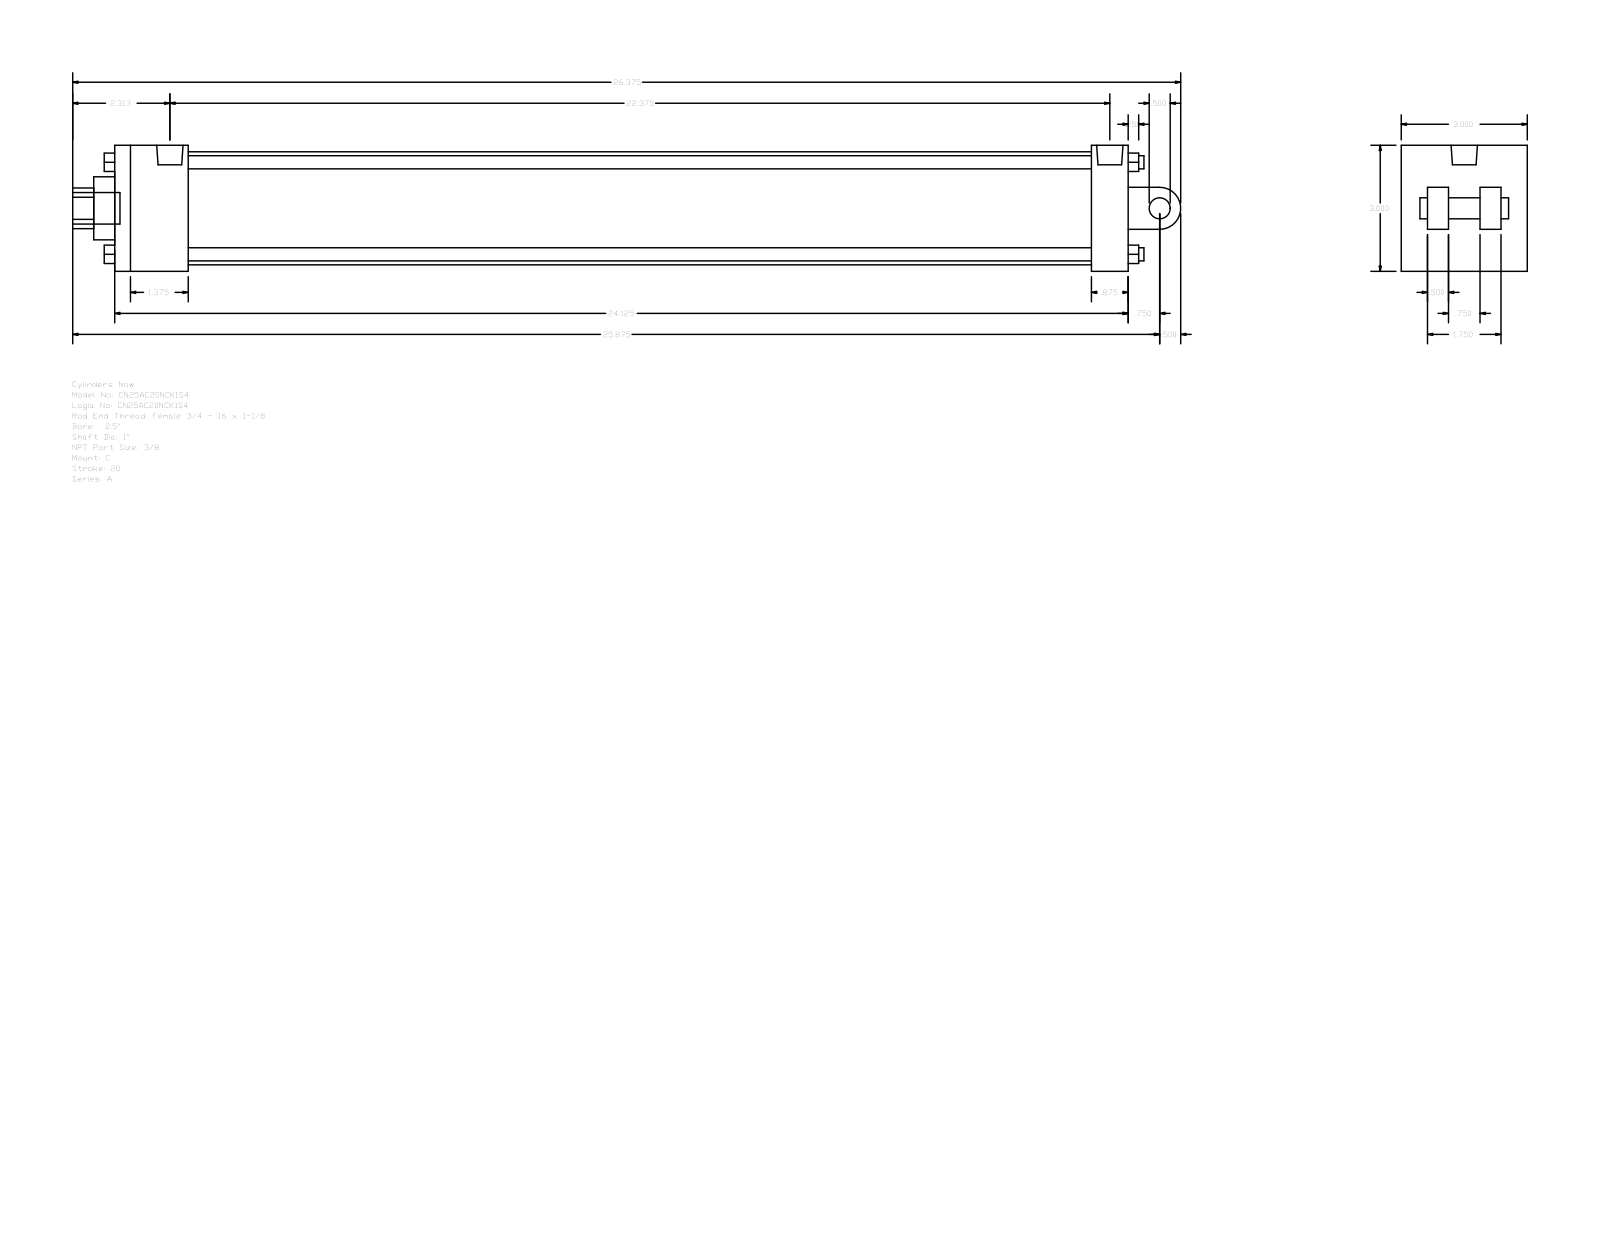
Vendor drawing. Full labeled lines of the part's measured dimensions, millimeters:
Part name (STEP PRODUCT): A_C__0250_1
STEP written by: GSSL Pune (CONFIG_CONTROL_DESIGN)
Units: millimetres
Bodies: 0 solids, 135 faces (102 planar, 33 cylindrical, 0 other)
Overall size (bounding box): 669.92 × 76.2 × 76.2
Round holes (diameter × count): ⌀5.56 ×2, ⌀15.93 ×1, ⌀25.4 ×1, ⌀38.1 ×1, ⌀68.33 ×1
Round bosses / shafts (diameter × count): ⌀7.94 ×4, ⌀5.56 ×2, ⌀19.05 ×1, ⌀15.93 ×1, ⌀12.7 ×1
Partial cylindrical surfaces — rounded edges, fillets, slot ends (radius × count): R12.29 ×1, R12.7 ×1
Main face-to-face distances: 76.2, 612.77, 12.7, 44.45, 590.55, 546.1, 568.32, 22.22, 15.87, 25.4
Hole centre spacings: 2.38
